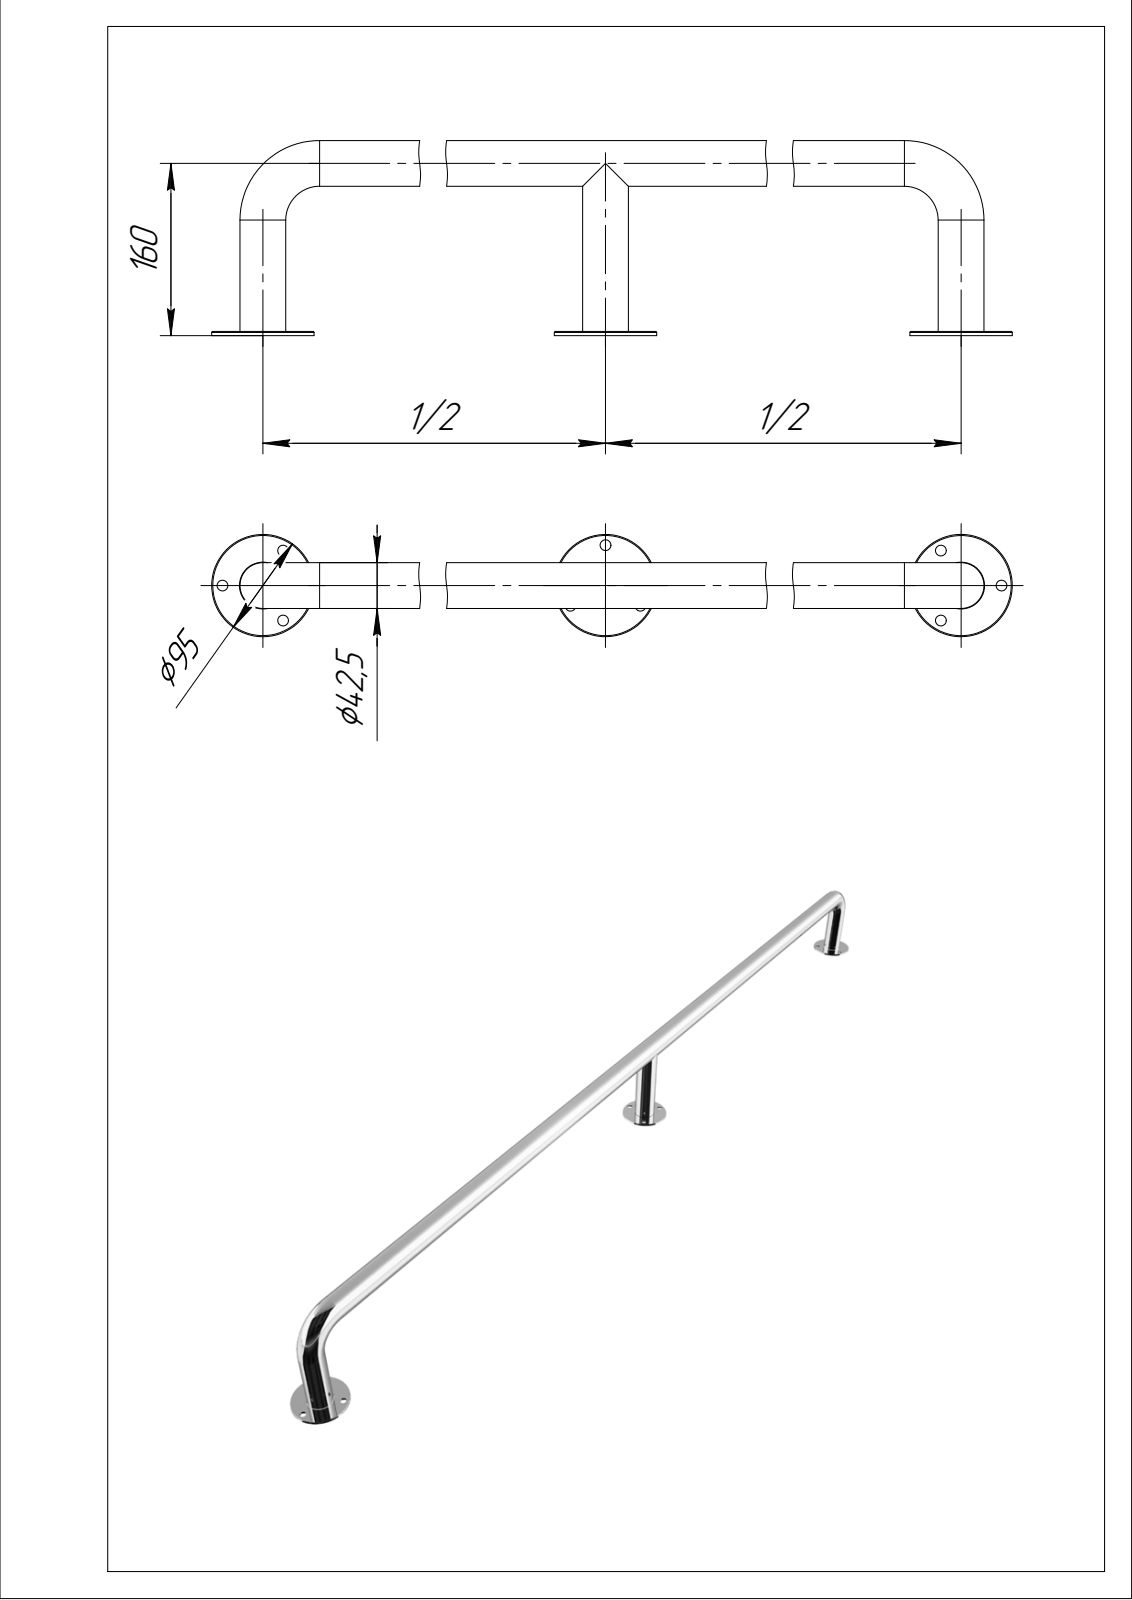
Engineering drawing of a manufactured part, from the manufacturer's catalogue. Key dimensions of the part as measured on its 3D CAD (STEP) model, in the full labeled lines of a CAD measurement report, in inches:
Part name (STEP PRODUCT): Сборка; Деталь; Фланец; Тр 2-42.5
STEP written by: ASCON Math Kernel (AUTOMOTIVE_DESIGN)
Units: inches
Bodies: 7 solids, 50 faces (13 planar, 27 cylindrical, 10 other)
Overall size (bounding box): 80.807 × 7.136 × 3.74
Volume: 24.56 in³ · Surface area: 1 033 in²
Round holes (diameter × count): ⌀0.394 ×9, ⌀1.594 ×3, ⌀1.713 ×2, ⌀0.236 ×1, ⌀1.555 ×1, ⌀1.673 ×1
Round bosses / shafts (diameter × count): ⌀3.74 ×3, ⌀1.673 ×3, ⌀1.535 ×1
Main face-to-face distances: 0.157, 0.472, 0.315, 6.693, 6.535, 6.22
Hole centre spacings: 1.476, 2.557, 37.817, 76.339, 77.816, 2.557, 36.52, 36.572
